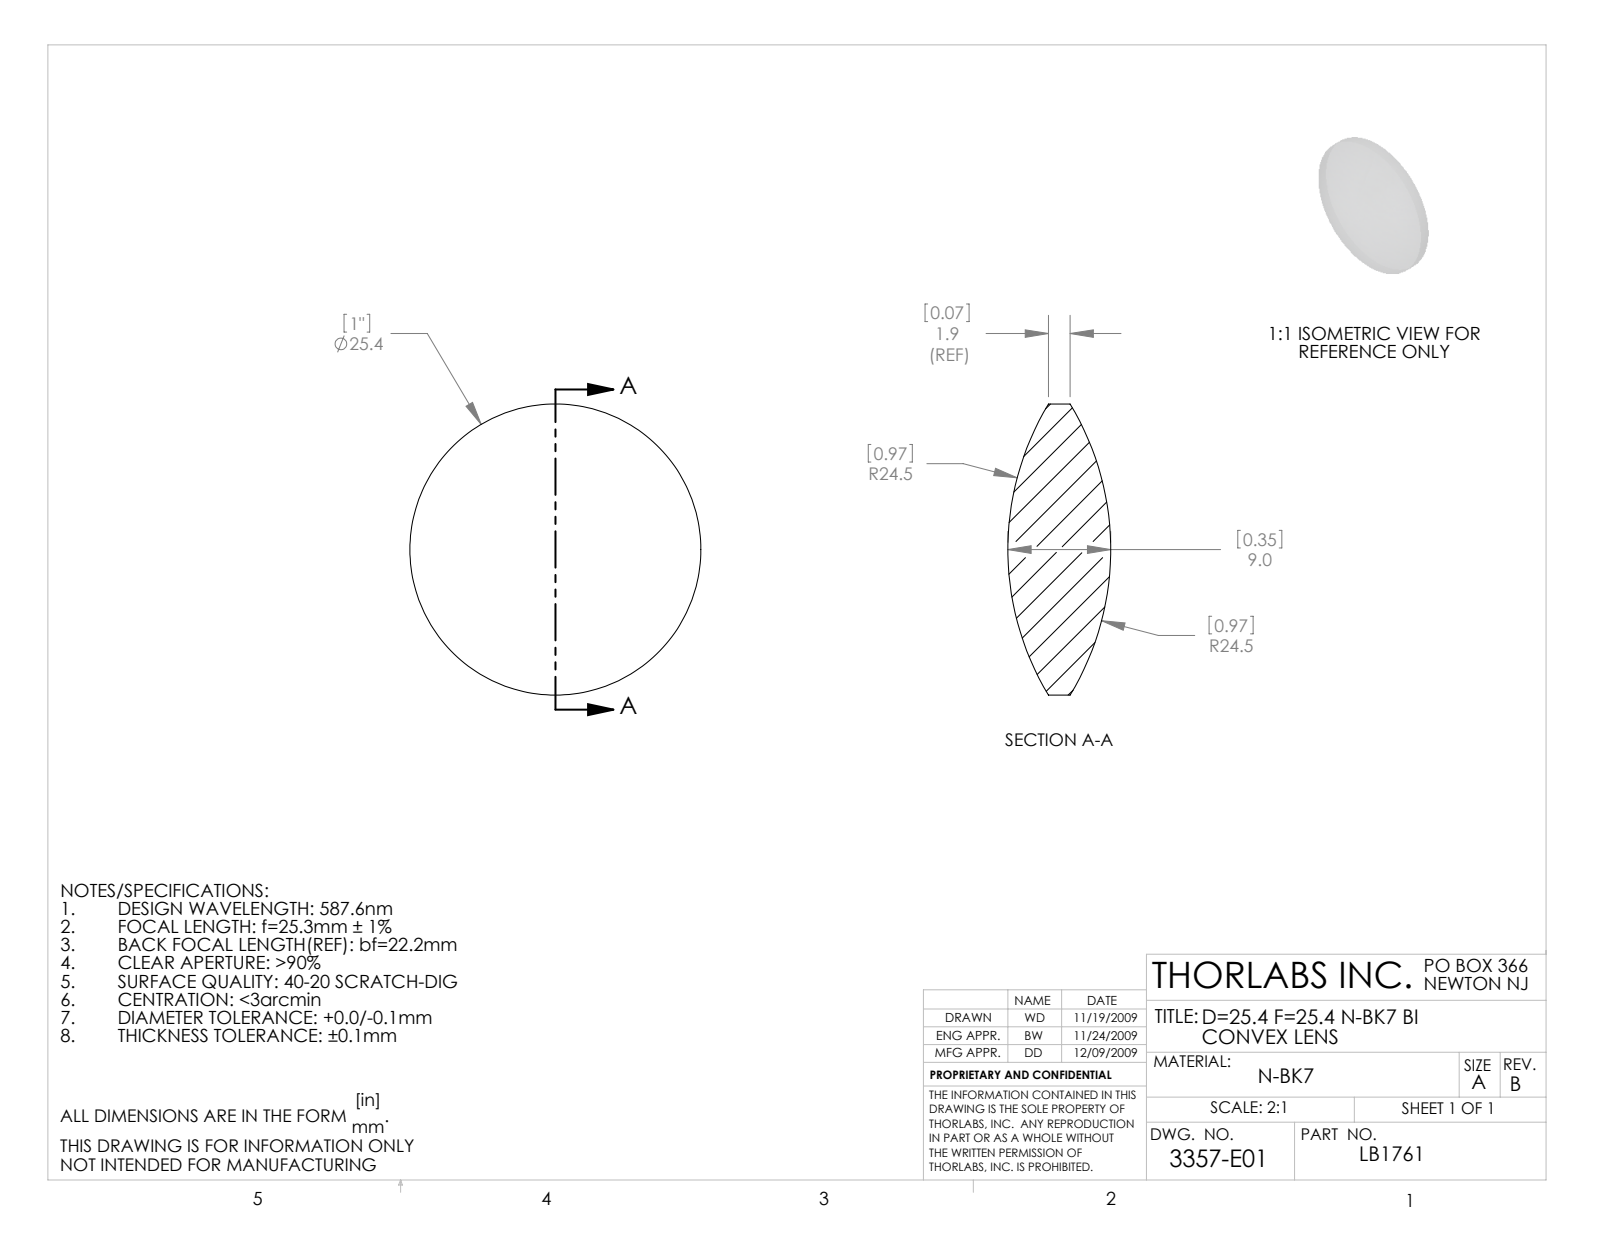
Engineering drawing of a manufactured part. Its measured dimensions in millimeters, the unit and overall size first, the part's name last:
Units: millimetres
Overall size (bounding box): 25.4 × 25.4 × 8.98
Round bosses / shafts (diameter × count): ⌀25.4 ×1
Volume: 2 801 mm³ · Surface area: 1 243 mm²
Bodies: 1 solid, 6 faces (0 planar, 2 cylindrical, 4 other)
Part name (STEP PRODUCT): 3357-E0W
STEP written by: SolidWorks 2009 (AUTOMOTIVE_DESIGN)
